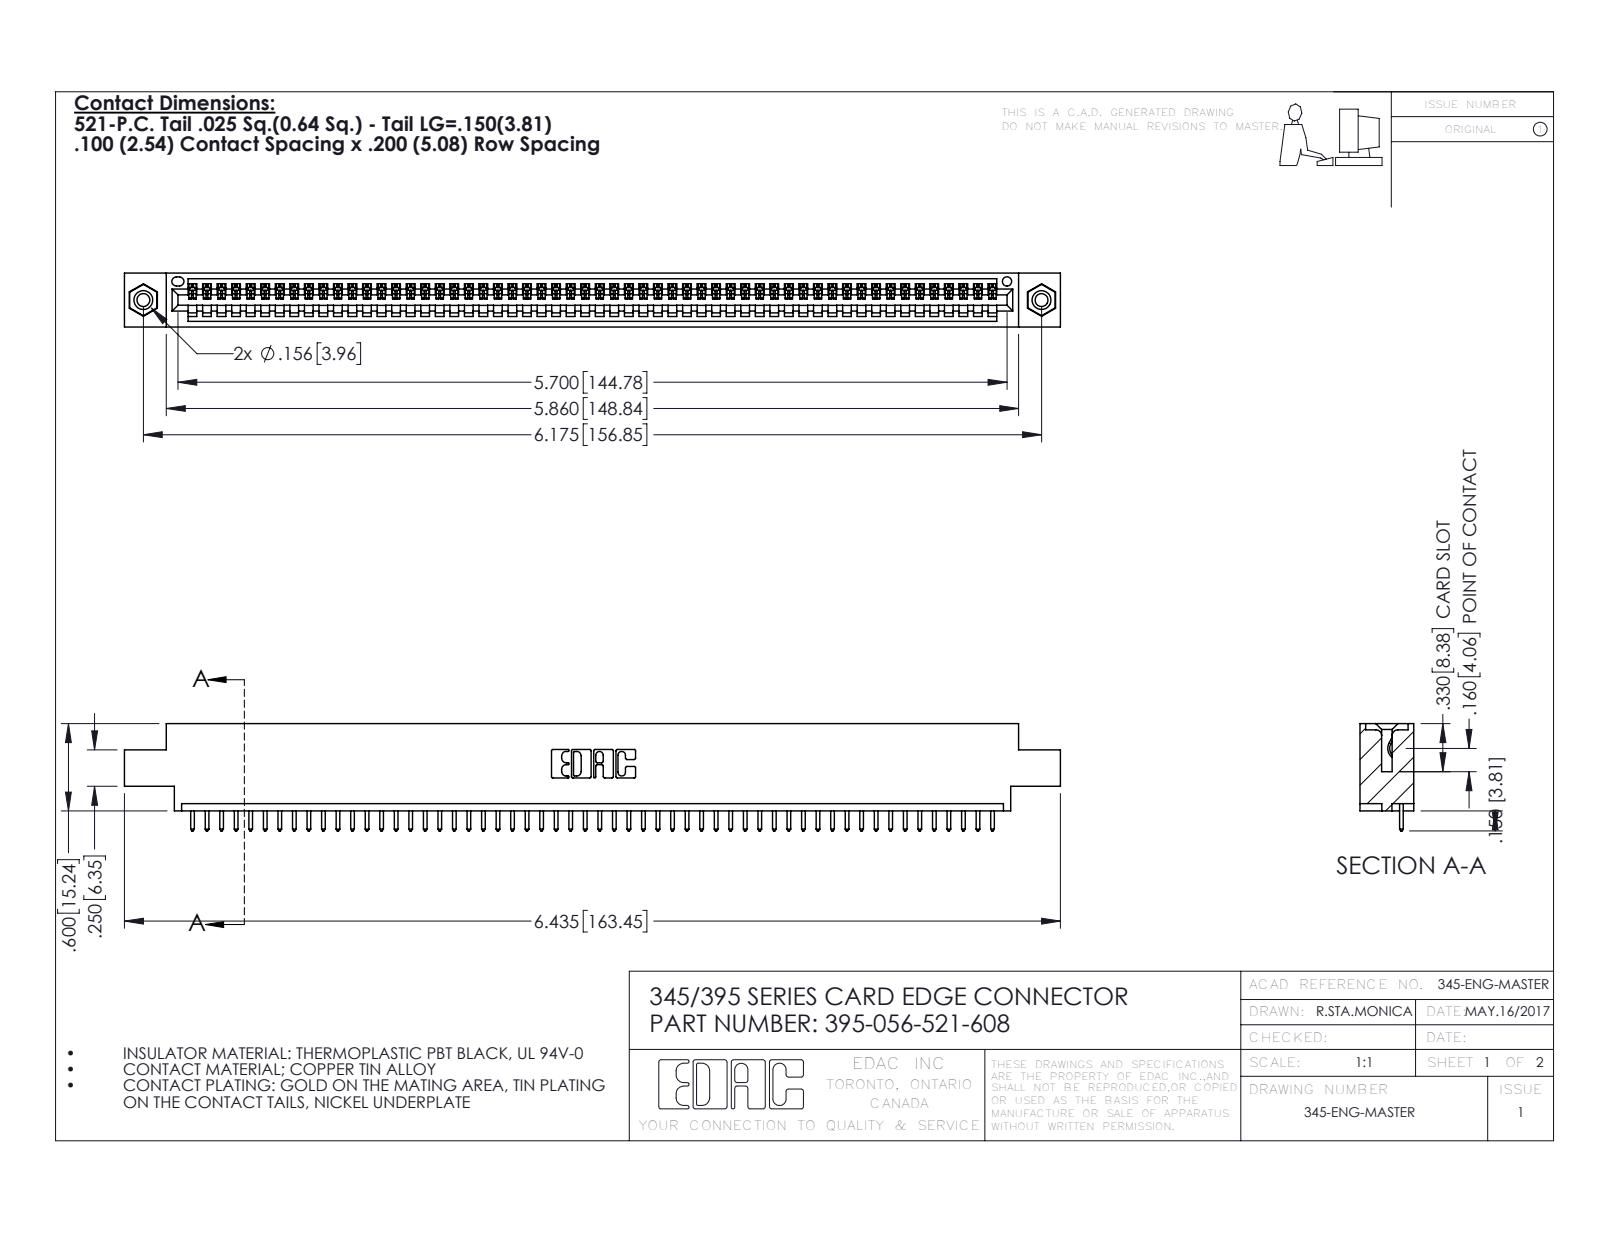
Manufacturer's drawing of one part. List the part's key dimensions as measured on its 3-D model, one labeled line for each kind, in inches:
Part name (STEP PRODUCT): 345-292-001_345-293-121; 345 Part_0.170 Offset - 0.156 Dia-TI; 395-056-521-608; 345-250-001_345-250-003-102
STEP written by: SolidWorks 2016 (CONFIG_CONTROL_DESIGN)
Units: inches
Bodies: 59 solids, 3438 faces (2356 planar, 1066 cylindrical, 16 other)
Overall size (bounding box): 6.435 × 0.737 × 0.37
Volume: 0.937 in³ · Surface area: 31.19 in²
Round holes (diameter × count): ⌀0.089 ×2, ⌀0.125 ×2, ⌀0.156 ×2, ⌀0.064 ×1
Round bosses / shafts (diameter × count): ⌀0.155 ×2
Partial cylindrical surfaces — rounded edges, fillets, slot ends (radius × count): R0.006 ×112, R0.01 ×112, R0.01 ×22, R0.007 ×6, R0.031 ×6, R0.026 ×3, R0.031 ×2, R0.04 ×2
Main face-to-face distances: 0.072, 0.298, 0.37, 0.2, 0.098, 0.272, 0.025, 0.225, 0.175, 0.149
Hole centre spacings: 0.27, 5.939, 6.175
